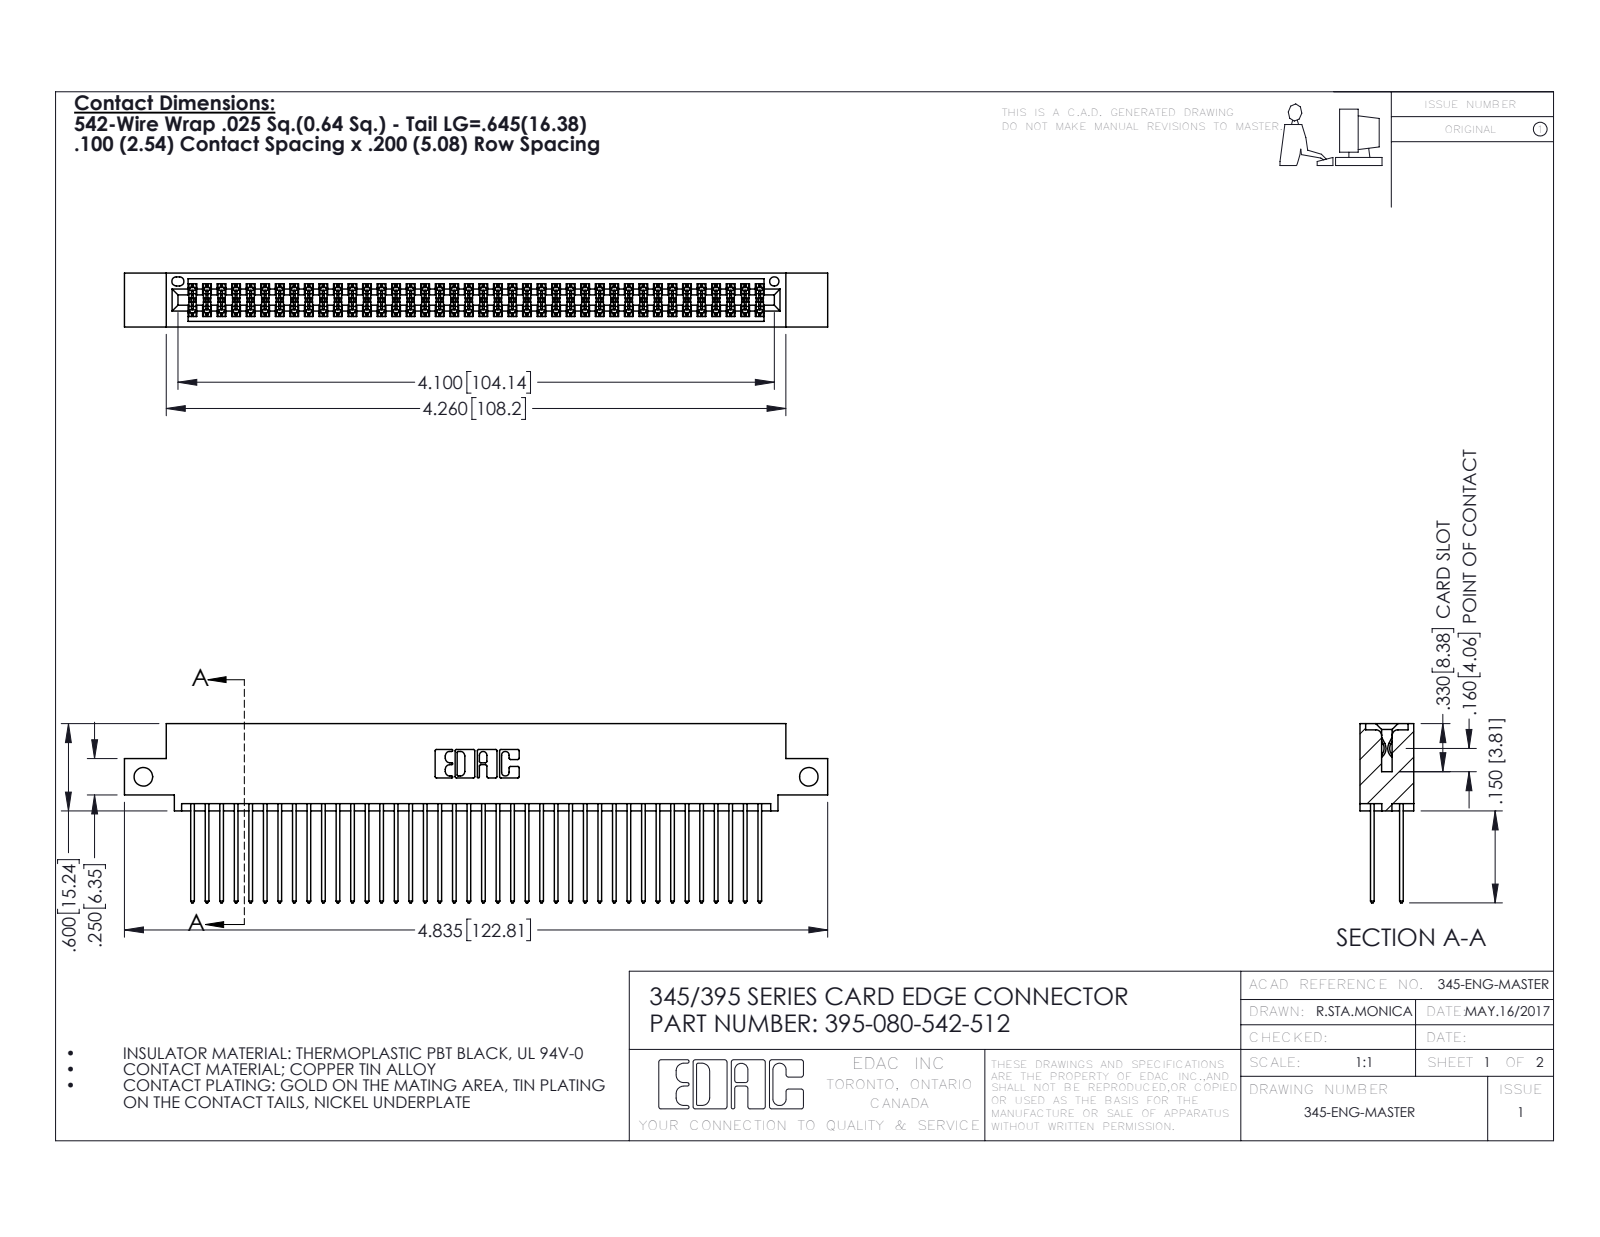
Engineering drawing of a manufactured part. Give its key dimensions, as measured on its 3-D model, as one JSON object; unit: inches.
{"part_name": "345-292-001_345-293-142; 395-080-542-512; 345 Part_0.110 Offset - Side Mount", "step_written_by": "SolidWorks 2016 (CONFIG_CONTROL_DESIGN)", "units": "inches", "bodies": {"solids": 81, "faces": 4130, "planar": 2724, "cylindrical": 1406, "other": 0}, "overall_size": [4.835, 1.232, 0.37], "volume_in3": 0.74, "surface_area_in2": 30.35, "round_holes": [[0.128, 2], [0.064, 1]], "partial_cylinders_radius": [[0.006, 120], [0.01, 80], [0.01, 22], [0.007, 6], [0.031, 6], [0.026, 3], [0.014, 2], [0.019, 2]], "face_to_face_distances": [0.298, 0.072, 0.2, 0.098, 0.272, 0.025, 0.225, 0.37, 0.175, 0.149], "hole_center_spacings": [4.575]}
